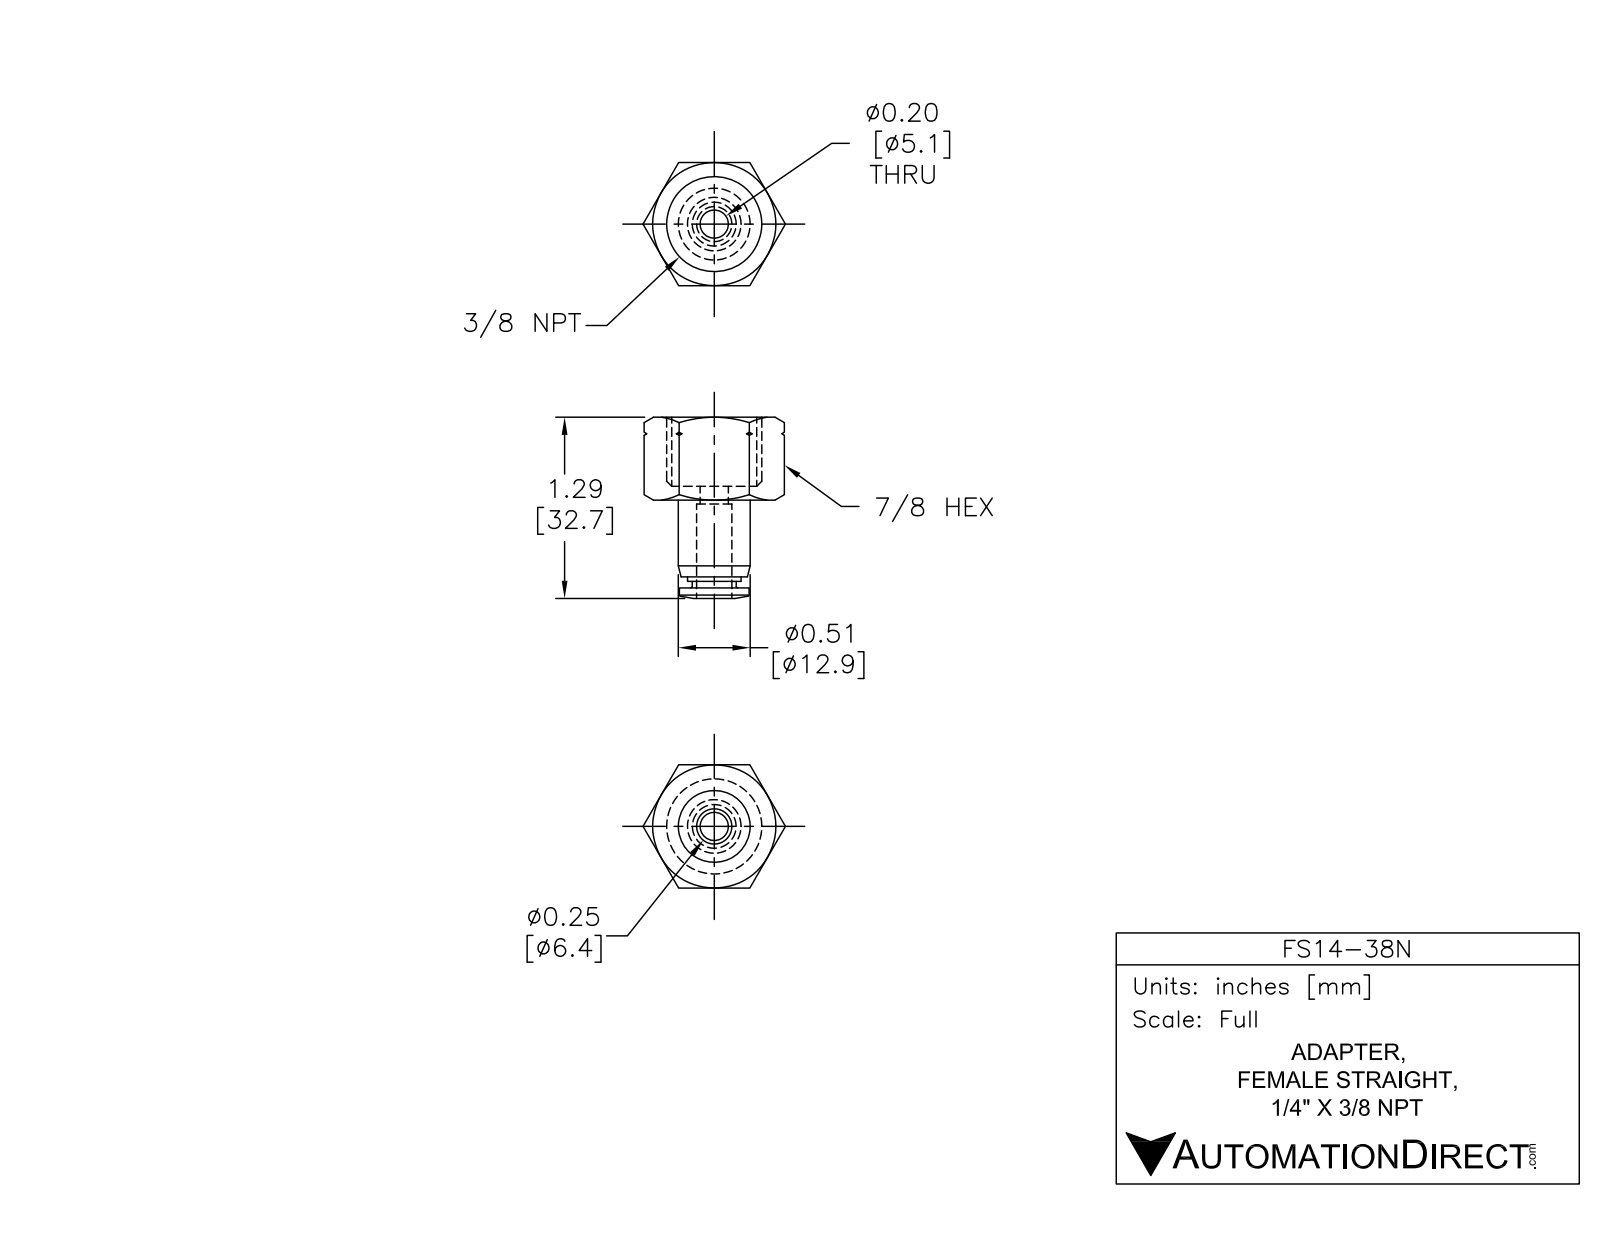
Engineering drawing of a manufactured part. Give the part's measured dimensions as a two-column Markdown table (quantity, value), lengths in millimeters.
| quantity | value |
| --- | --- |
| part name | FS14-38N |
| STEP written by | SolidWorks 2015 (AUTOMOTIVE_DESIGN) |
| units | millimeters |
| bodies | 1 solid, 63 faces (13 planar, 12 cylindrical, 38 other) |
| overall size | 32.8 × 25.4 × 22 |
| volume | 5 030 mm³ |
| surface area | 3 745 mm² |
| round holes (diameter × count) | 5 × 1, 6.6 × 1 |
| round bosses / shafts (diameter × count) | 13 × 1, 12.6 × 1, 9.7 × 1, 8 × 1 |
| main face-to-face distances | 22, 2.5, 15, 12.5, 15.9, 30.9, 18.4, 28.9, 16.4, 13.9 |
